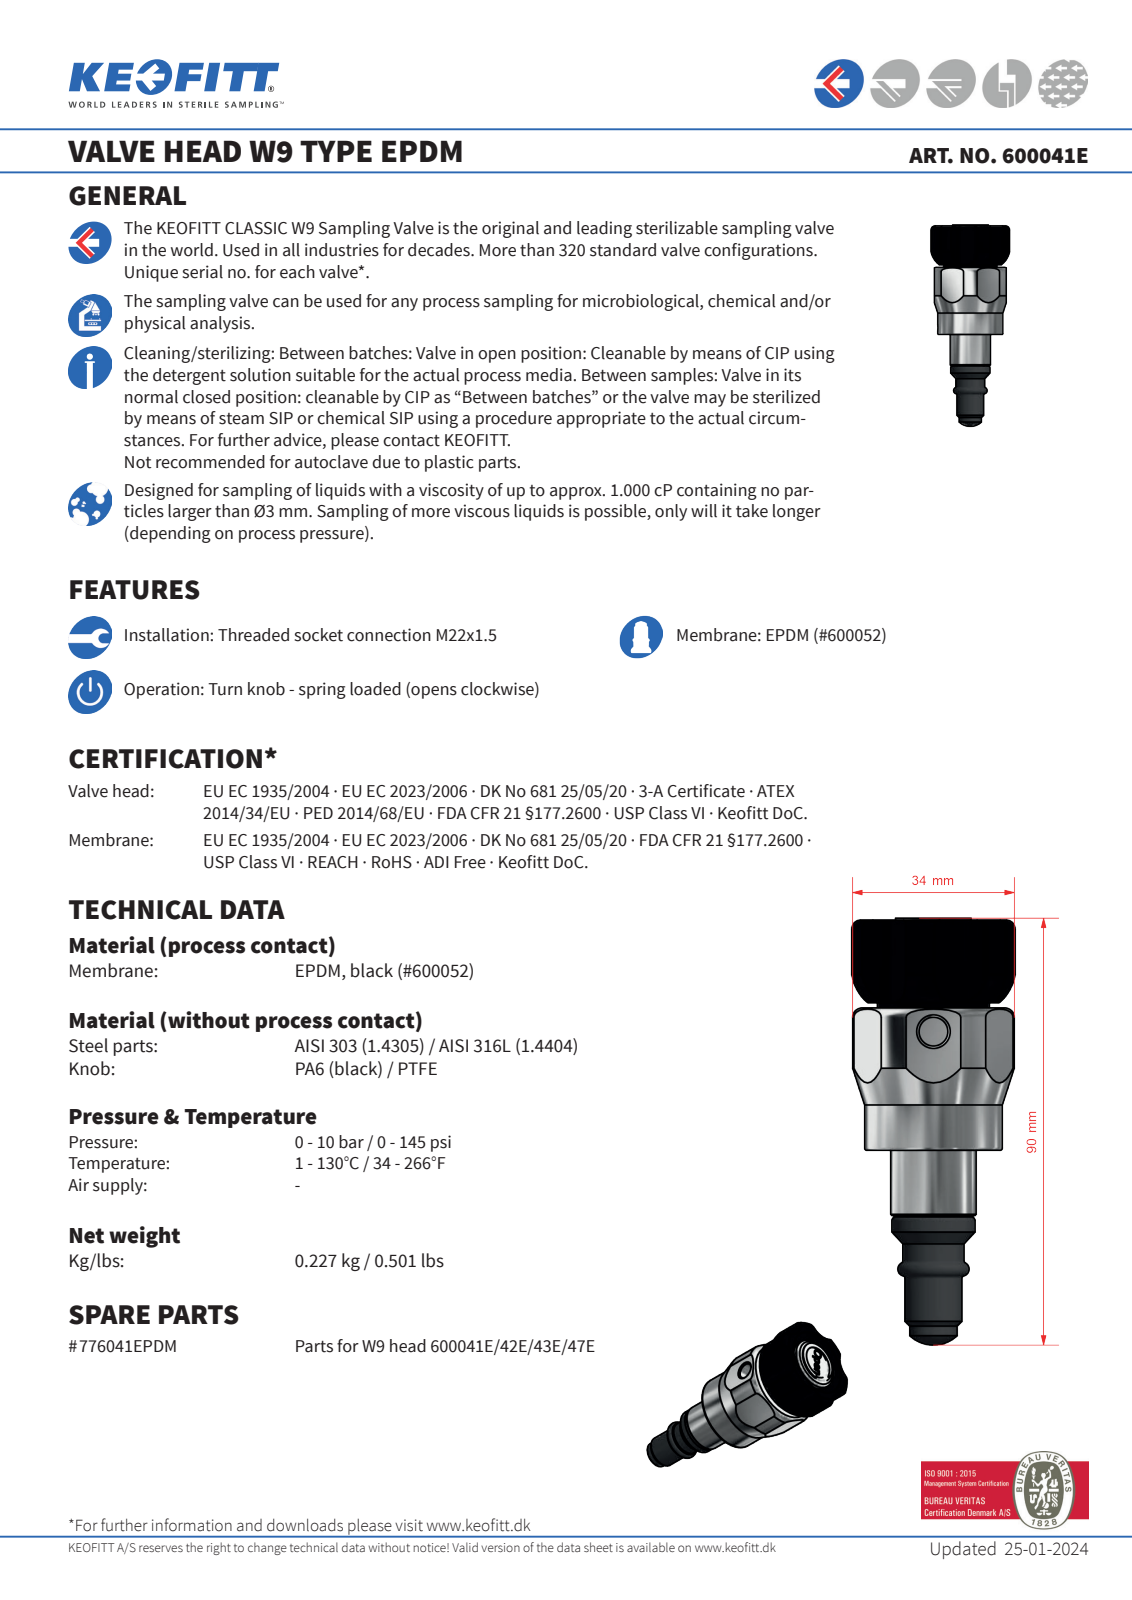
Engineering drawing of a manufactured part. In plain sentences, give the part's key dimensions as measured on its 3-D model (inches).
Its 3-D file was written by "Autodesk Inventor 2008 (AUTOMOTIVE_DESIGN)". It is 1 solid with 163 faces: 57 planar, 40 cylindrical and 66 other. Overall it measures 3.543 by 1.378 by 1.355 inches. Its volume is 2.646 cubic inches and its surface area 15.35 square inches. Round holes: 1 of diameter 0.12, 1 of diameter 0.238, 1 of diameter 0.732, 1 of diameter 0.811, 1 of diameter 0.921. Round bosses or shafts: 3 of diameter 0.118, 1 of diameter 1.142, 1 of diameter 0.929, 1 of diameter 0.787, 1 of diameter 0.709, 1 of diameter 0.689, 1 of diameter 0.508, 1 of diameter 0.472. Partial cylindrical surfaces (rounded edges, fillets, slot ends): 6 of radius 0.315, 1 of radius 0.276, 1 of radius 0.529, 1 of radius 0.669, 1 of radius 0.689. The main face-to-face distances are 1.26, 0.709, 1.89, 1.181, 0.02, 0.728, 1.909, 1.897, 1.877, 1.169. The hole center spacings are 0.079.
